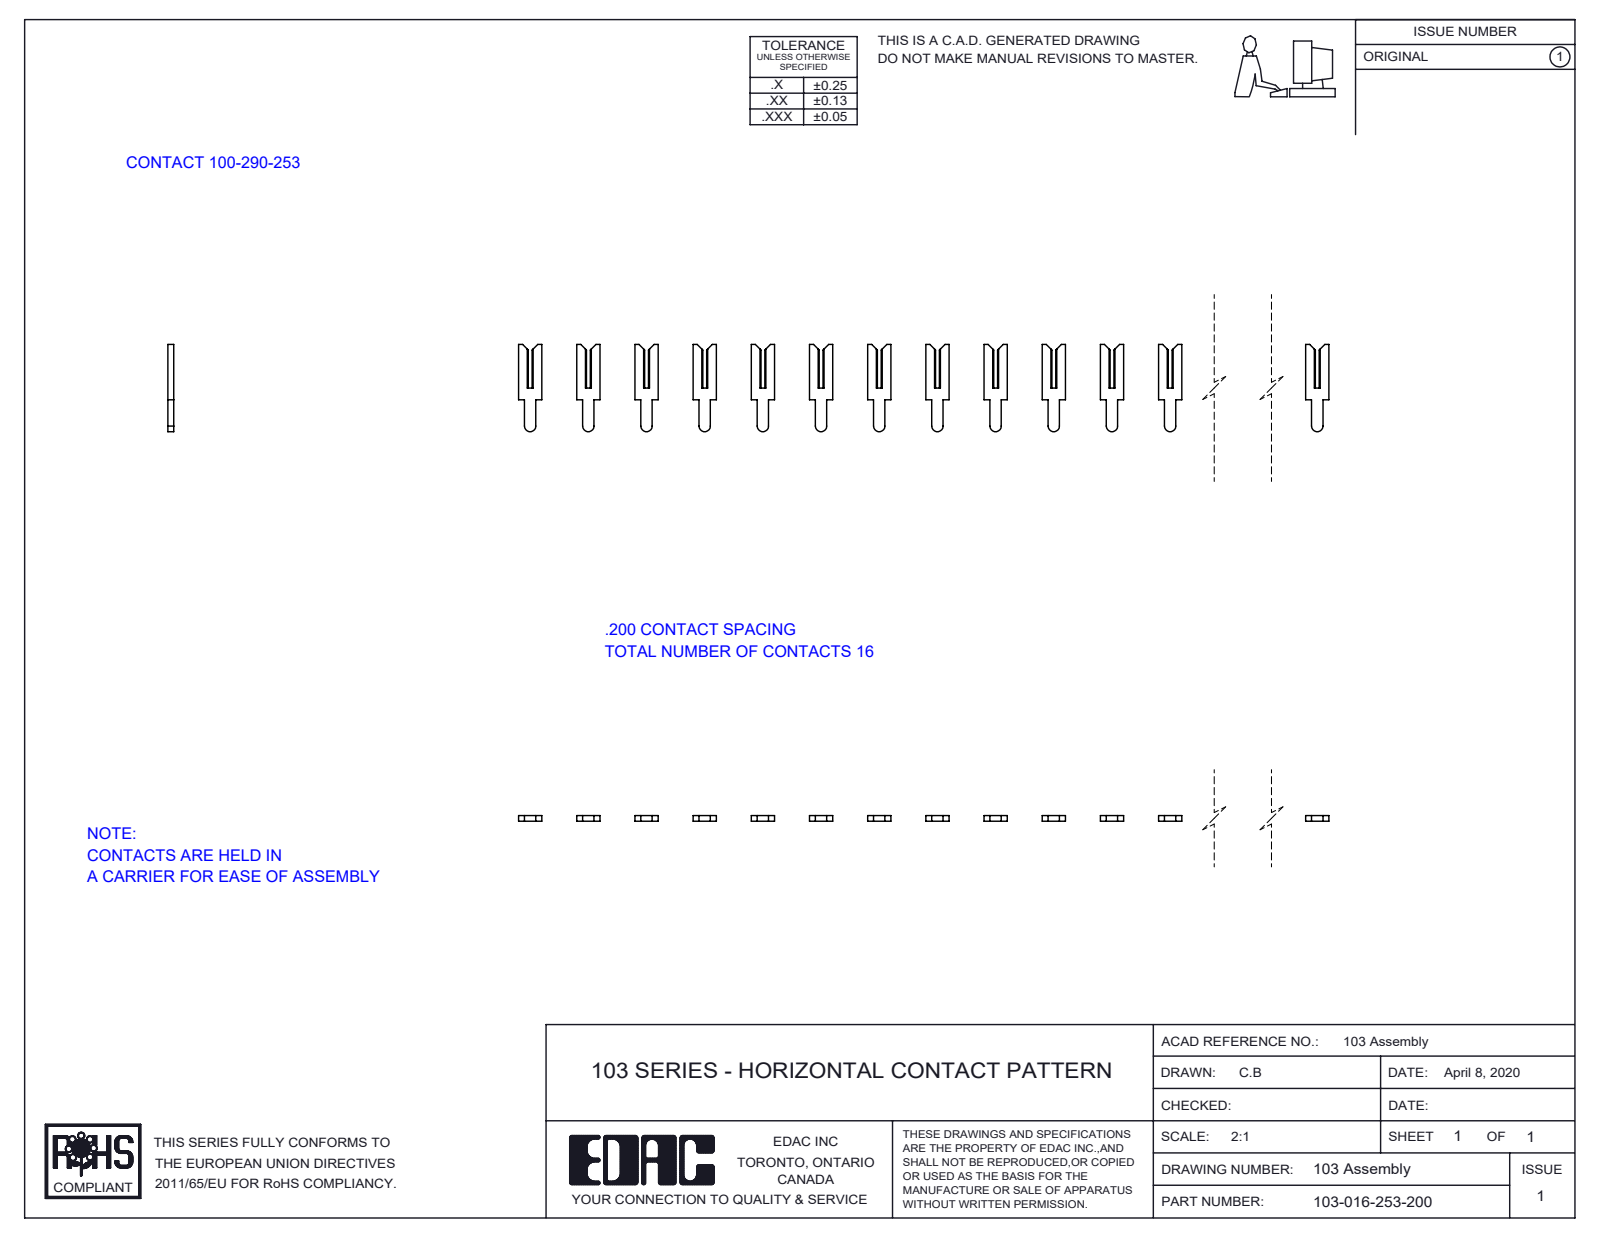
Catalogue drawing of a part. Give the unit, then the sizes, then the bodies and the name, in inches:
Units: inches
Overall size (bounding box): 3.08 × 0.3 × 0.02
Partial cylindrical surfaces — rounded edges, fillets, slot ends (radius × count): R0.019 ×16
Main face-to-face distances: 0.02, 0.2, 0.4, 0.6, 0.141, 0.8, 1, 1.2, 0.848, 0.283
Volume: 0.005 in³ · Surface area: 0.853 in²
Bodies: 16 solids, 320 faces (304 planar, 16 cylindrical, 0 other)
Part name (STEP PRODUCT): 100-290-001_100-290-253; 103-016-253-200
STEP written by: SolidWorks 2016 (CONFIG_CONTROL_DESIGN)
